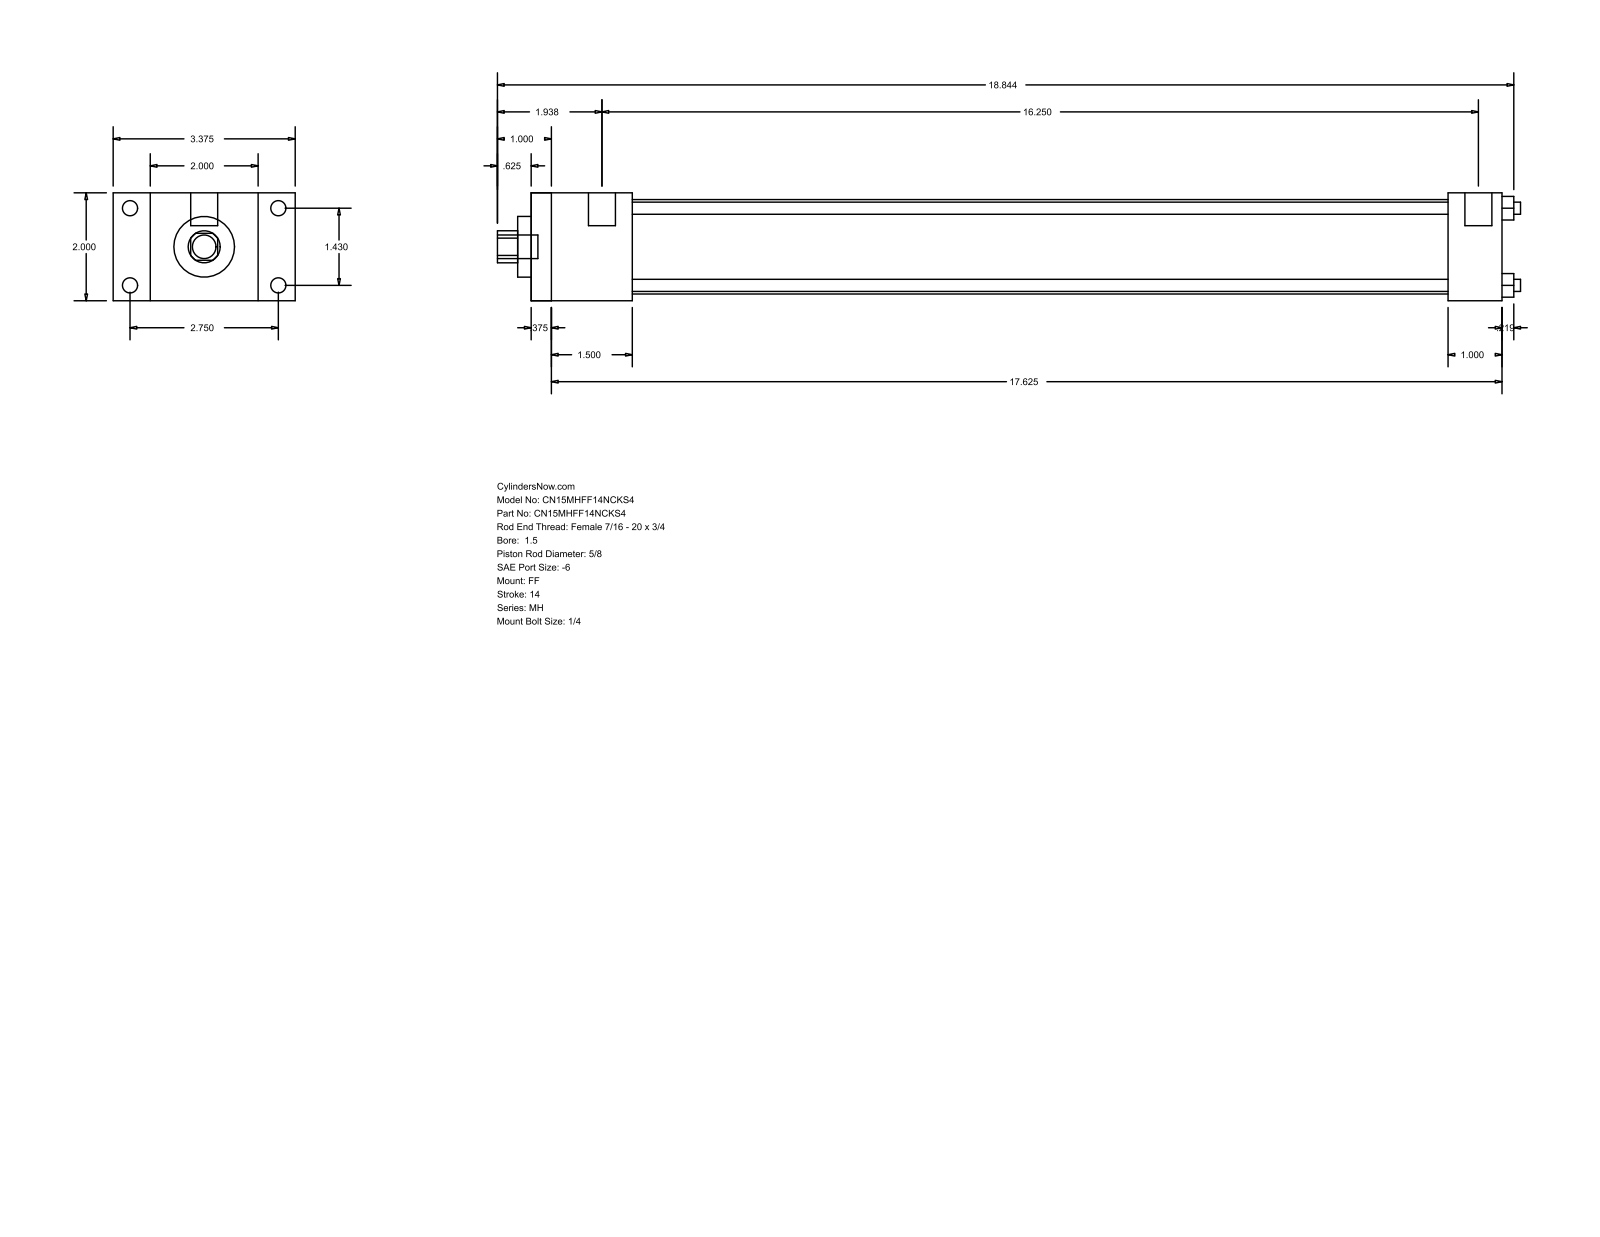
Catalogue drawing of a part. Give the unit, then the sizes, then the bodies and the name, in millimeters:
Units: millimetres
Overall size (bounding box): 481.81 × 85.72 × 50.8
Round holes (diameter × count): ⌀5.71 ×4, ⌀15.88 ×1, ⌀28.57 ×1, ⌀44.45 ×1
Round bosses / shafts (diameter × count): ⌀7.14 ×4, ⌀5.56 ×4, ⌀12.7 ×2, ⌀11.11 ×1
Partial cylindrical surfaces — rounded edges, fillets, slot ends (radius × count): R7.54 ×1
Main face-to-face distances: 50.8, 457.19, 9.52, 447.67, 17.46, 68.26, 47.62, 38.1, 409.57, 431.8
Hole centre spacings: 25.68, 36.32, 51.36
Bodies: 0 solids, 92 faces (64 planar, 28 cylindrical, 0 other)
Part name (STEP PRODUCT): MH_FF__0150_0.625
STEP written by: GSSL Pune (CONFIG_CONTROL_DESIGN)
